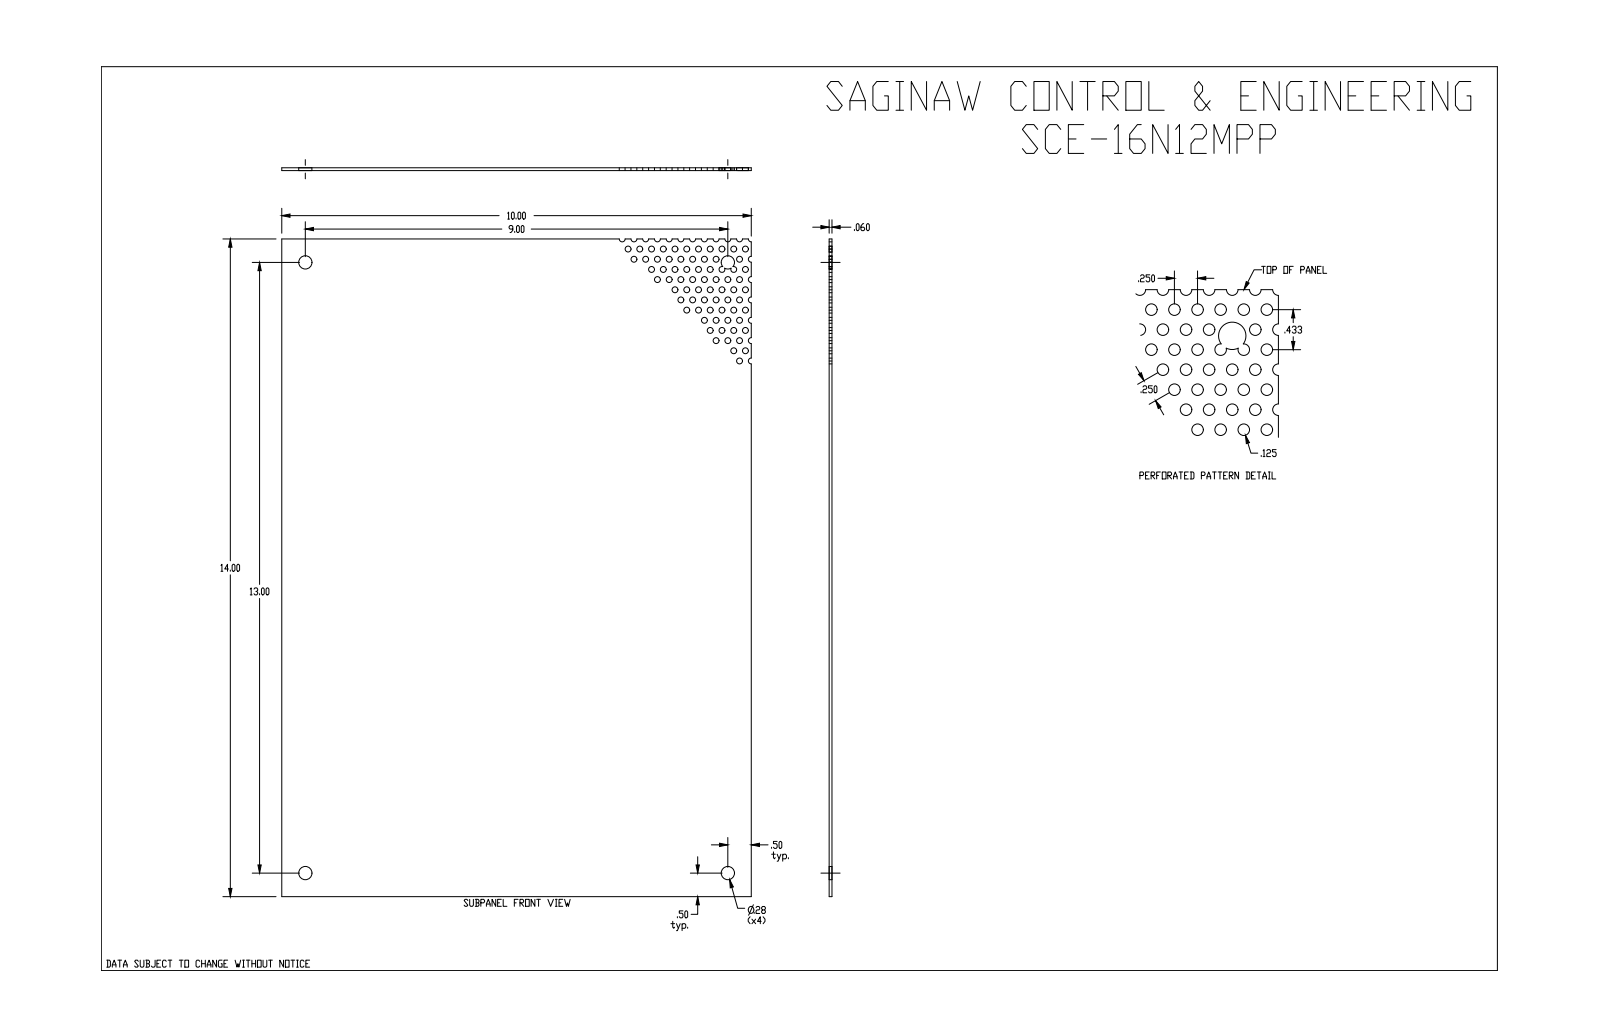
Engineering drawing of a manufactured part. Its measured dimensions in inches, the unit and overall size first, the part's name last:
Units: inches
Overall size (bounding box): 14 × 10 × 0.06
Round holes (diameter × count): ⌀0.125 ×63, ⌀0.125 ×7, ⌀0.281 ×4
Partial cylindrical surfaces — rounded edges, fillets, slot ends (radius × count): R0.063 ×10, R0.062 ×8
Main face-to-face distances: 0.06, 10, 14
Hole centre spacings: 0.25, 0.661, 0.5, 0.433, 1.323, 0.433, 1.09, 0.75
Volume: 8.327 in³ · Surface area: 282.4 in²
Bodies: 1 solid, 116 faces (23 planar, 93 cylindrical, 0 other)
Part name (STEP PRODUCT): SCE-16N12MPP
STEP written by: SolidWorks 2019 (CONFIG_CONTROL_DESIGN)
